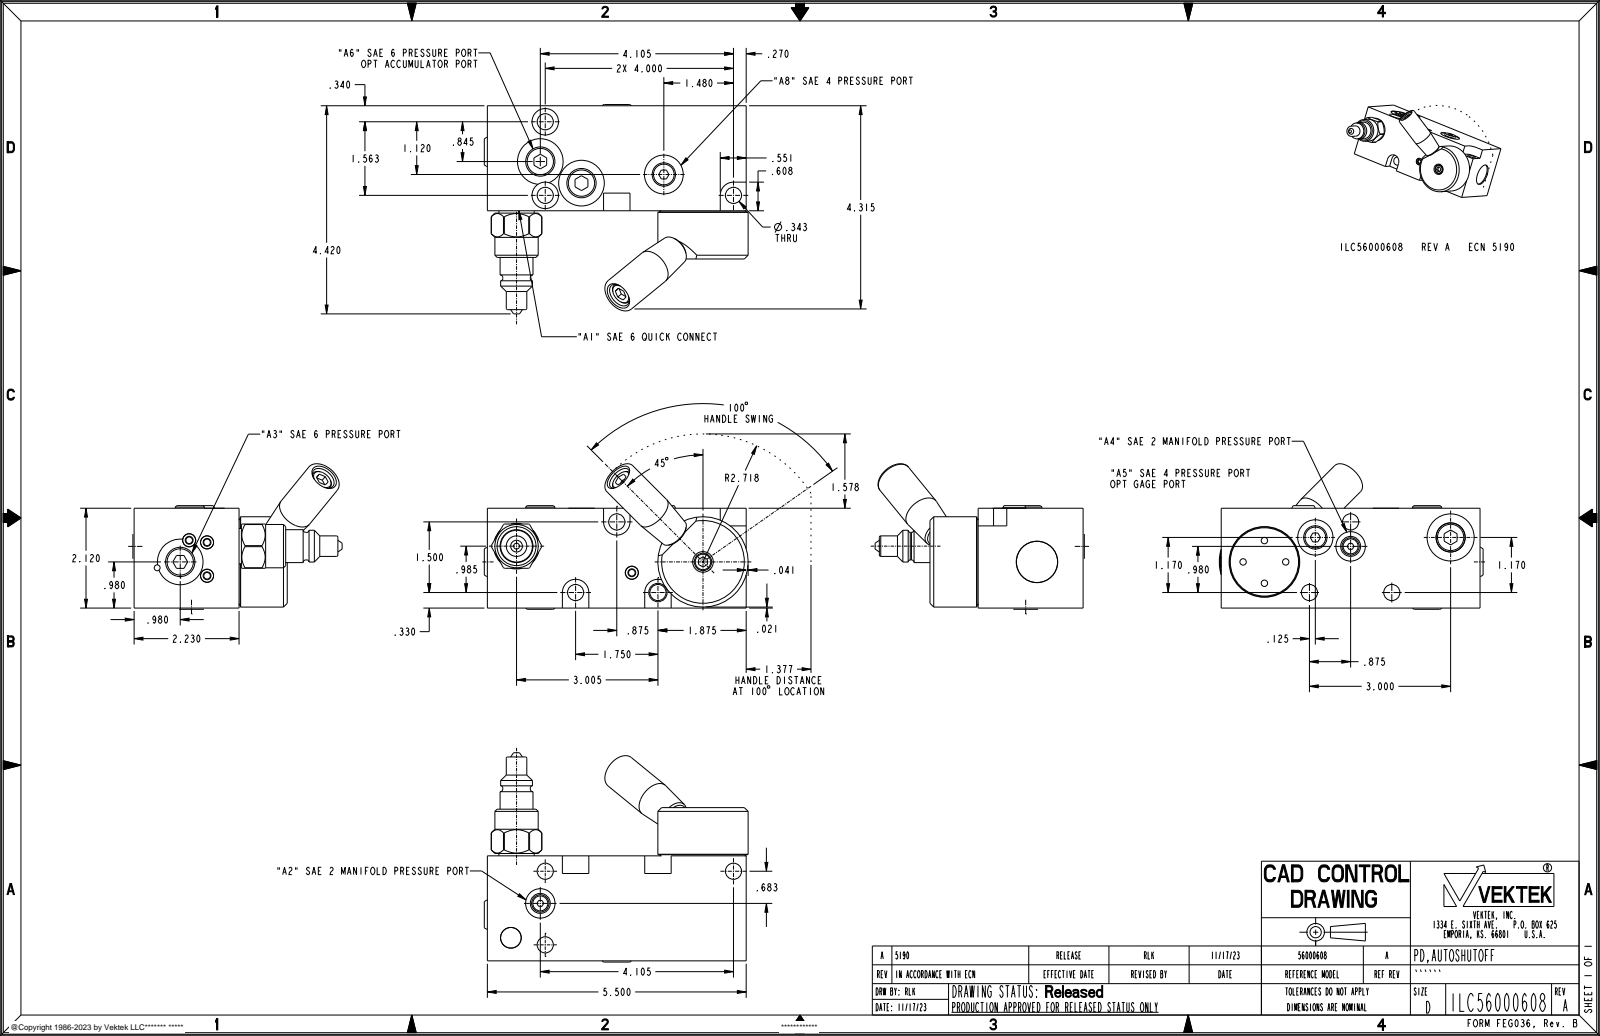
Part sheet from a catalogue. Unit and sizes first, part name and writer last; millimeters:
Units: millimetres
Overall size (bounding box): 176.3 × 112.9 × 94.6
Round holes (diameter × count): ⌀8.7 ×6, ⌀4.8 ×5, ⌀13.1 ×5, ⌀3.5 ×4, ⌀3.6 ×4, ⌀4 ×4, ⌀4.2 ×4, ⌀7.1 ×4, ⌀24.6 ×4, ⌀10 ×3, ⌀19.1 ×3, ⌀4.7 ×2
Round bosses / shafts (diameter × count): ⌀7 ×4, ⌀6.3 ×4, ⌀12.2 ×2, ⌀6.1 ×2, ⌀48.7 ×1, ⌀43.3 ×1, ⌀37.6 ×1, ⌀28.6 ×1
Partial cylindrical surfaces — rounded edges, fillets, slot ends (radius × count): R2.8 ×4, R7.1 ×4, R7.1 ×1, R13.6 ×1, R15.5 ×1, R21.1 ×1
Main face-to-face distances: 53.8, 56.6, 139.7, 82.7, 26, 0.6, 56, 82, 2.5, 54.7
Hole centre spacings: 5.4, 7.7, 16.2, 9.6, 15.2, 6.1, 8.9, 10.8
Volume: 407 900 mm³ · Surface area: 90 450 mm²
Bodies: 2 solids, 855 faces (208 planar, 253 cylindrical, 394 other)
Part name (STEP PRODUCT): ILC56000608
STEP written by: CREO PARAMETRIC BY PTC INC, 2021164 (AUTOMOTIVE_DESIGN)
